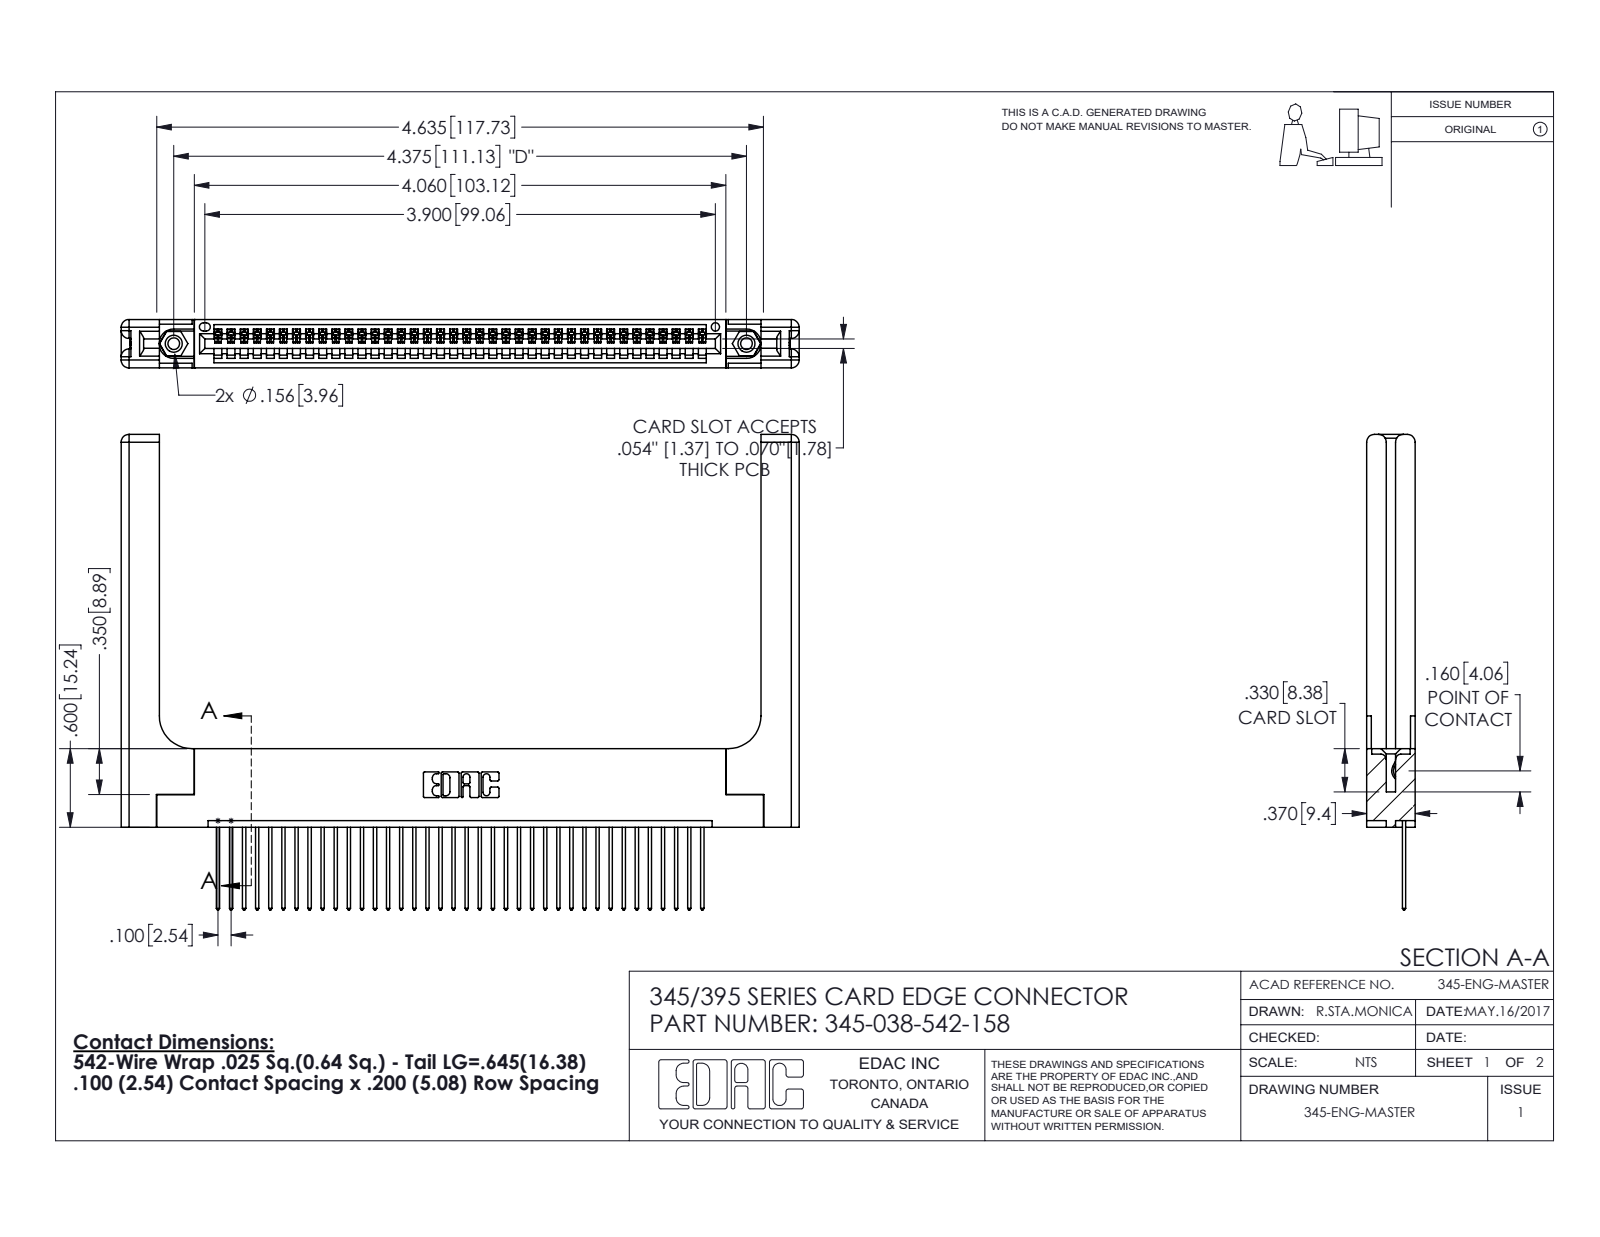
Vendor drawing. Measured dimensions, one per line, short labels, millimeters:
name: 345 Part_Flush Mounting Lugs - 0.156 Dia-TH; 345-220-058_345-220-058; 345-250-001_345-250-001-102; 345-038-542-158 (+1 more)
written by: SolidWorks 2016 (CONFIG_CONTROL_DESIGN)
unit: mm
bodies: 43 solids, 2586 faces (1748 planar, 778 cylindrical, 60 other)
size: 131.5 × 92.3 × 9.4
volume: 21 060 mm³; area: 22 460 mm²
holes: 2× ⌀2.3, 2× ⌀3.2, 2× ⌀4, 1× ⌀1.6
bosses: 2× ⌀3.9
rounds: 76× R0.2, 76× R0.3, 22× R0.3, 16× R1.5, 6× R0.2, 6× R0.8, 3× R0.7, 2× R0.8
face distances: 1.8, 9.4, 7.6, 2.5, 6.9, 0.6, 5.1, 3.8, 3.8, 5.7
hole spacings: 6.9, 105.1, 111.1
